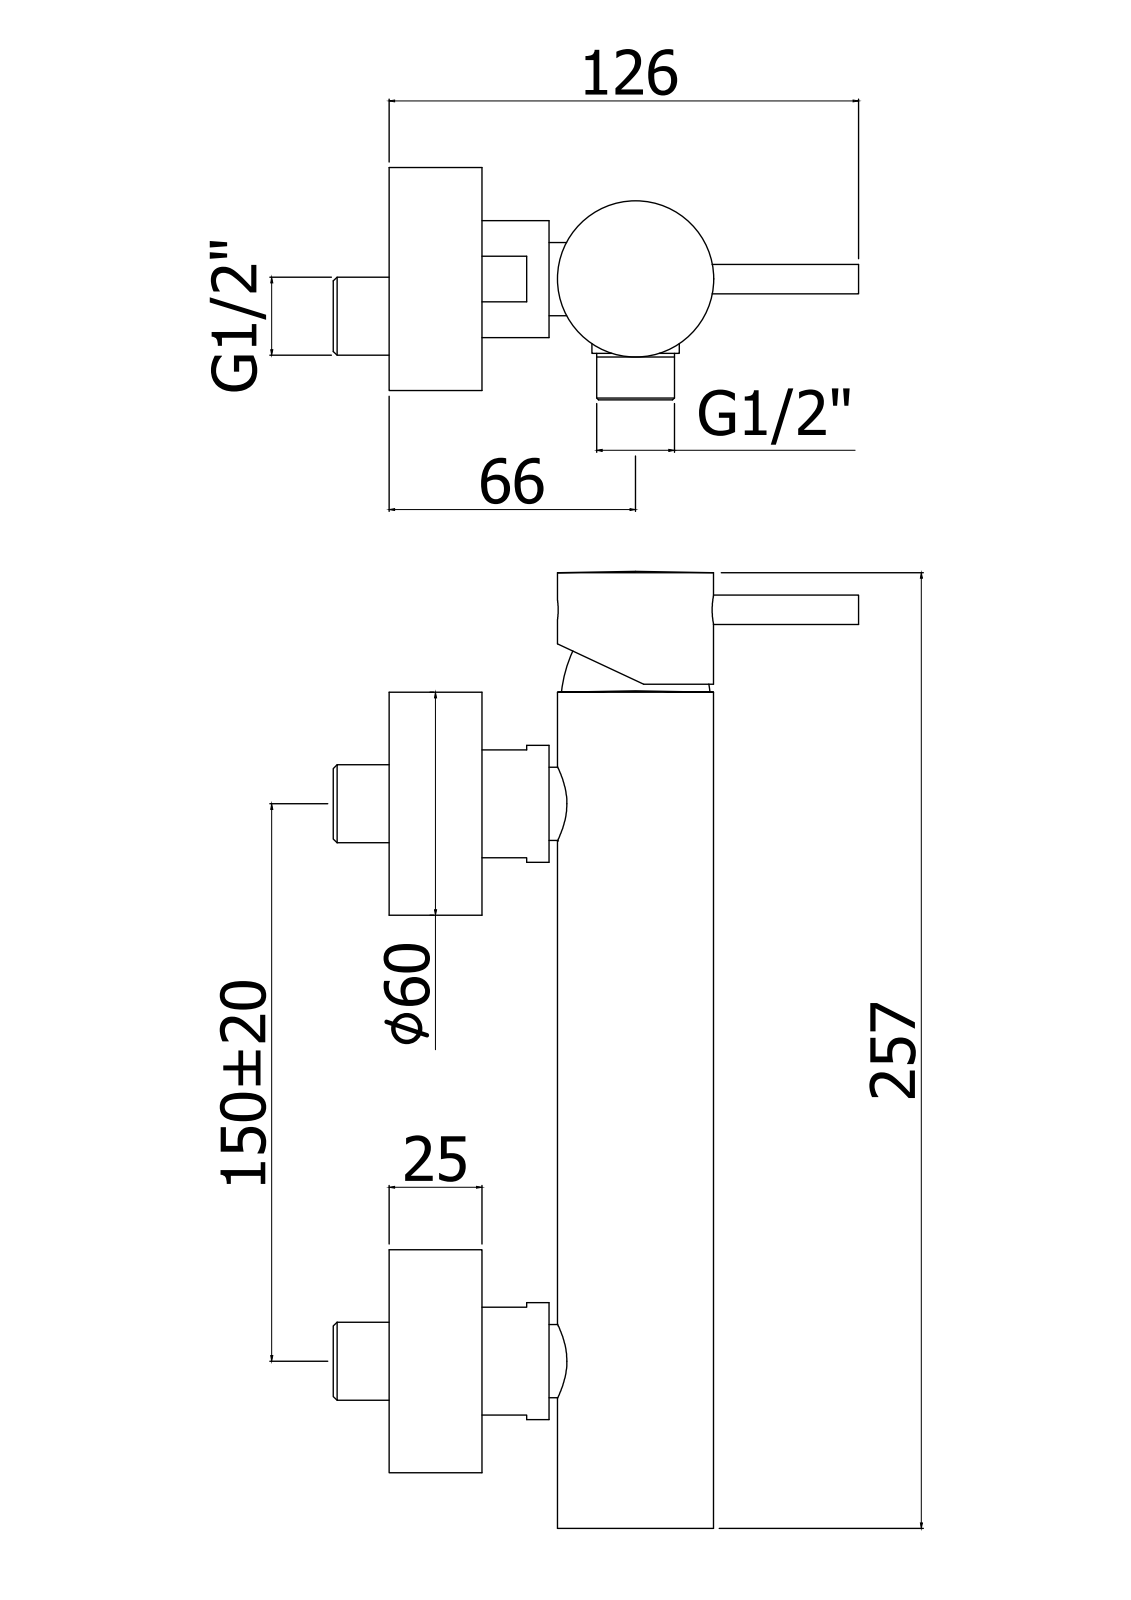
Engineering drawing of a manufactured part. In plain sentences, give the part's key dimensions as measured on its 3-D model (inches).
The part is named "BI168LCR". Its 3-D file was written by "CREO PARAMETRIC BY PTC INC, 2020044 (CONFIG_CONTROL_DESIGN)". It is 1 solid with 1261 faces: 693 planar, 357 cylindrical and 211 other. Overall it measures 10.587 by 4.926 by 2.48 inches. Its volume is 21.48 cubic inches and its surface area 182.6 square inches. Round holes: 6 of diameter 0.295, 3 of diameter 0.315, 3 of diameter 0.354, 3 of diameter 0.472, 3 of diameter 0.657, 2 of diameter 0.157, 2 of diameter 0.413, 2 of diameter 0.709, 2 of diameter 0.787, 2 of diameter 0.965, 2 of diameter 2.165, 1 of diameter 0.118. Round bosses or shafts: 2 of diameter 2.343, 2 of diameter 1.634, 2 of diameter 1.24, 2 of diameter 0.945, 2 of diameter 0.925, 2 of diameter 0.776, 1 of diameter 1.378, 1 of diameter 1.37. Partial cylindrical surfaces (rounded edges, fillets, slot ends): 44 of radius 0.02, 11 of radius 0.006, 9 of radius 0.012, 4 of radius 0.039, 4 of radius 0.276, 2 of radius 0.177, 2 of radius 0.313, 1 of radius 0.207. The main face-to-face distances are 0.185, 0.709, 0.894, 0.787, 0.972, 1.681, 1.256, 0.394, 0.118, 0.098. The hole center spacings are 0.551, 0.028, 0.035, 0.333, 0.335, 0.335, 0.337, 0.339.
